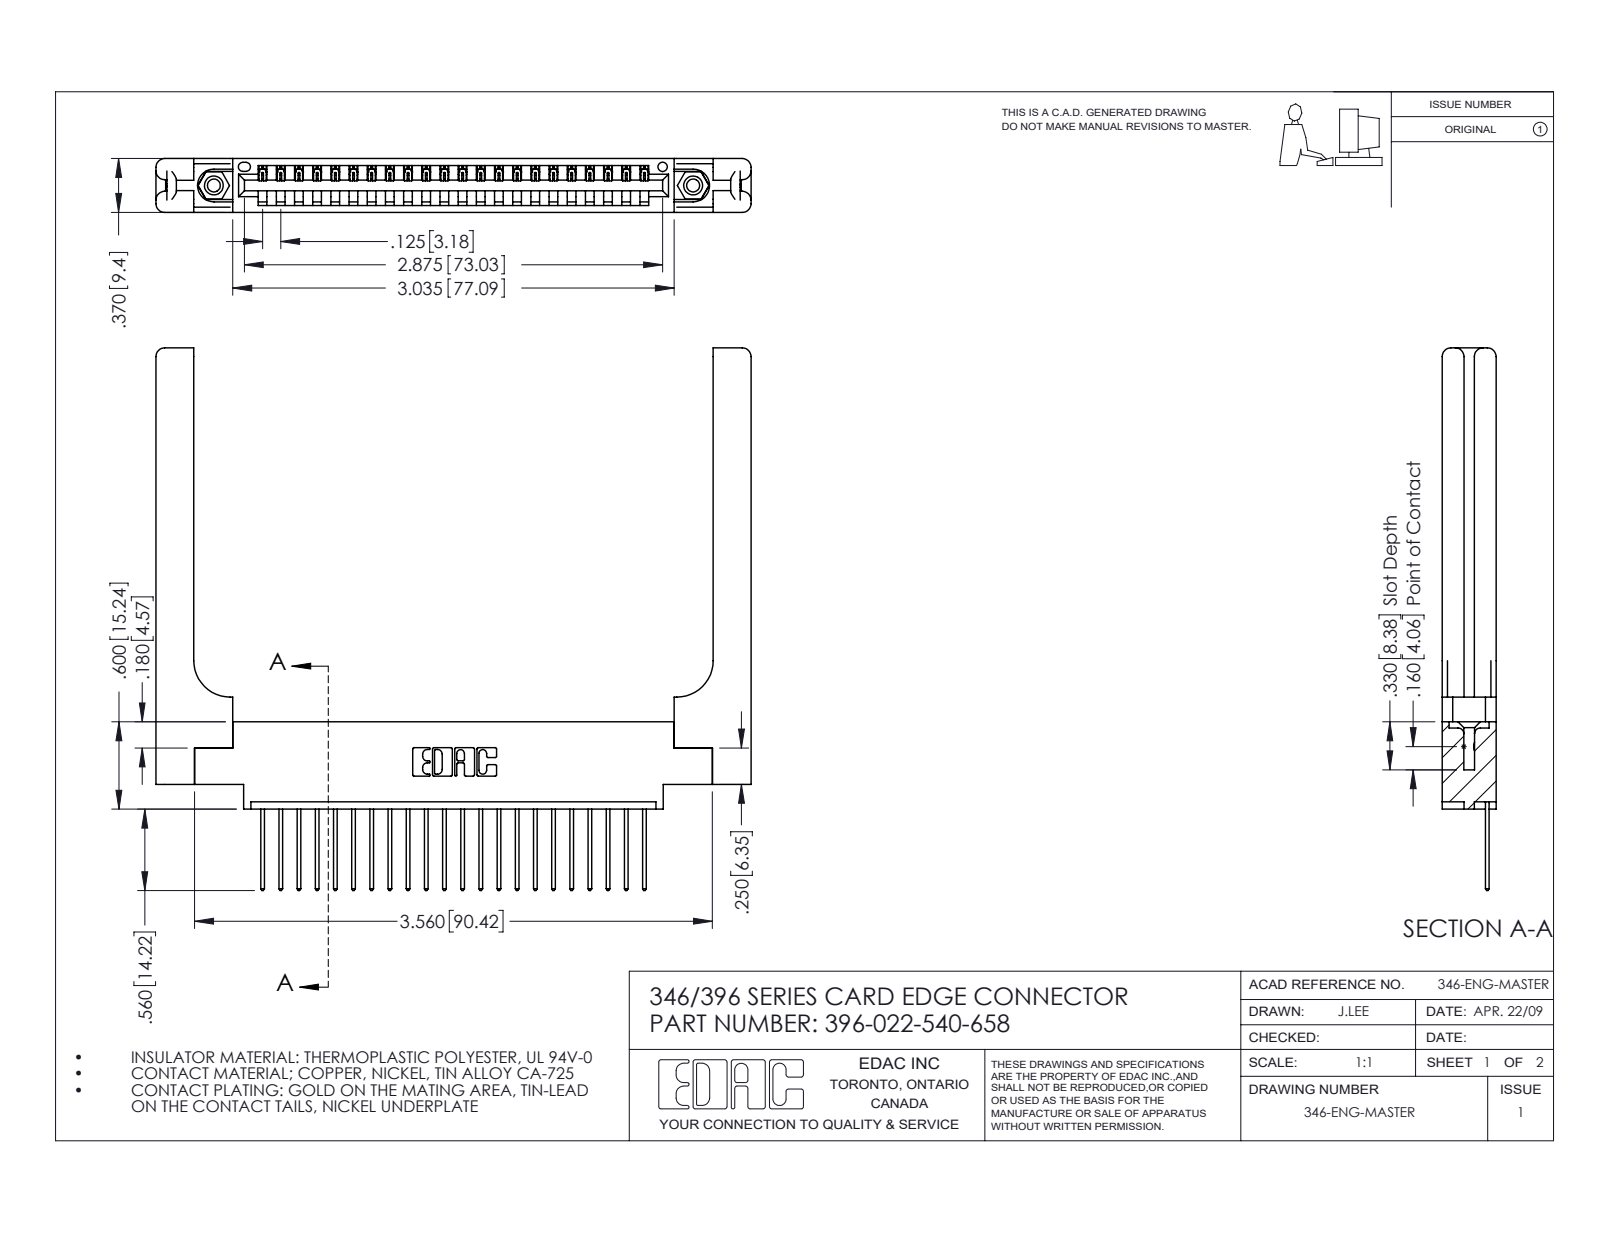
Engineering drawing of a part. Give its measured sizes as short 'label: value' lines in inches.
name: 346 Part_0.170 Offset - 0.156 Dia-TH; 345-250-001_345-250-001-102; 345-292-001_345-293-140; 396-022-540-658 (+1 more)
written by: SolidWorks 2016 (CONFIG_CONTROL_DESIGN)
unit: in
bodies: 27 solids, 1658 faces (1108 planar, 490 cylindrical, 60 other)
size: 4.091 × 3.73 × 0.37
volume: 1.05 in³; area: 27.02 in²
holes: 2× ⌀0.089, 2× ⌀0.125, 2× ⌀0.156, 1× ⌀0.064
bosses: 2× ⌀0.155
rounds: 44× R0.006, 44× R0.01, 22× R0.01, 16× R0.06, 6× R0.007, 6× R0.031, 3× R0.026, 2× R0.03
face distances: 0.37, 0.072, 0.048, 0.322, 0.15, 0.148, 0.25, 0.298, 0.025, 0.102
hole spacings: 0.246, 3.087, 3.295
